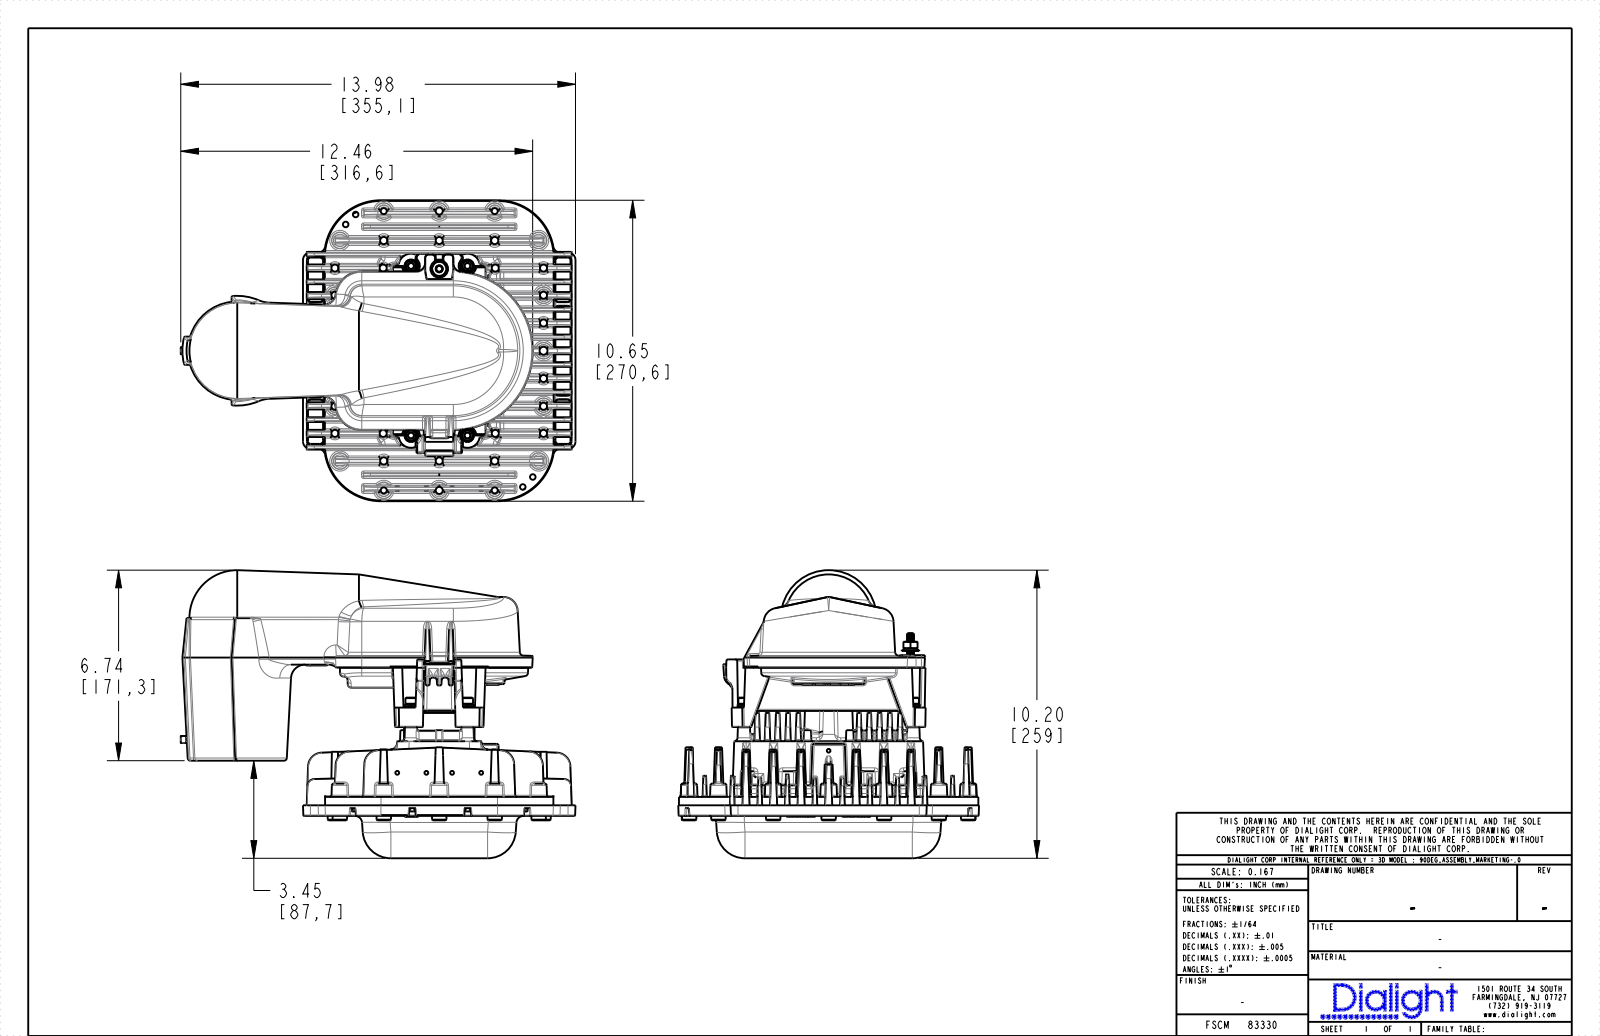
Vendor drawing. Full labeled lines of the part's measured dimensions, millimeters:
Part name (STEP PRODUCT): 3950HZC200100; 3050HZC2008EXC; 4700HZA2000000; 6000HZC201800_MCMASTER (+8 more)
STEP written by: CREO PARAMETRIC BY PTC INC, 2021304 (CONFIG_CONTROL_DESIGN)
Units: millimetres
Bodies: 38 solids, 10724 faces (2378 planar, 4147 cylindrical, 4199 other)
Overall size (bounding box): 355.1 × 270.6 × 259
Volume: 2 681 000 mm³ · Surface area: 933 500 mm²
Round holes (diameter × count): ⌀3.5 ×6, ⌀5 ×4, ⌀5.4 ×4, ⌀6.4 ×4, ⌀6.5 ×4, ⌀2.5 ×3, ⌀3.2 ×2, ⌀4.2 ×2, ⌀3.3 ×1, ⌀5 ×1, ⌀6.5 ×1, ⌀6.7 ×1
Round bosses / shafts (diameter × count): ⌀13 ×16, ⌀8 ×16, ⌀6.4 ×16, ⌀5.4 ×14, ⌀11.6 ×4, ⌀11.4 ×4, ⌀10 ×4, ⌀9.8 ×4
Partial cylindrical surfaces — rounded edges, fillets, slot ends (radius × count): R0.4 ×268, R0.1 ×264, R0.8 ×124, R1.3 ×120, R0.3 ×115, R1.5 ×108, R0.2 ×96, R0.5 ×93
Main face-to-face distances: 24.7, 74.3, 99, 49.5, 49.5, 173.3, 123.7, 148.5, 24.8, 11.3
Hole centre spacings: 45.8, 80.3, 117.1, 12.7, 25.5, 26.2, 38.1, 49.3
